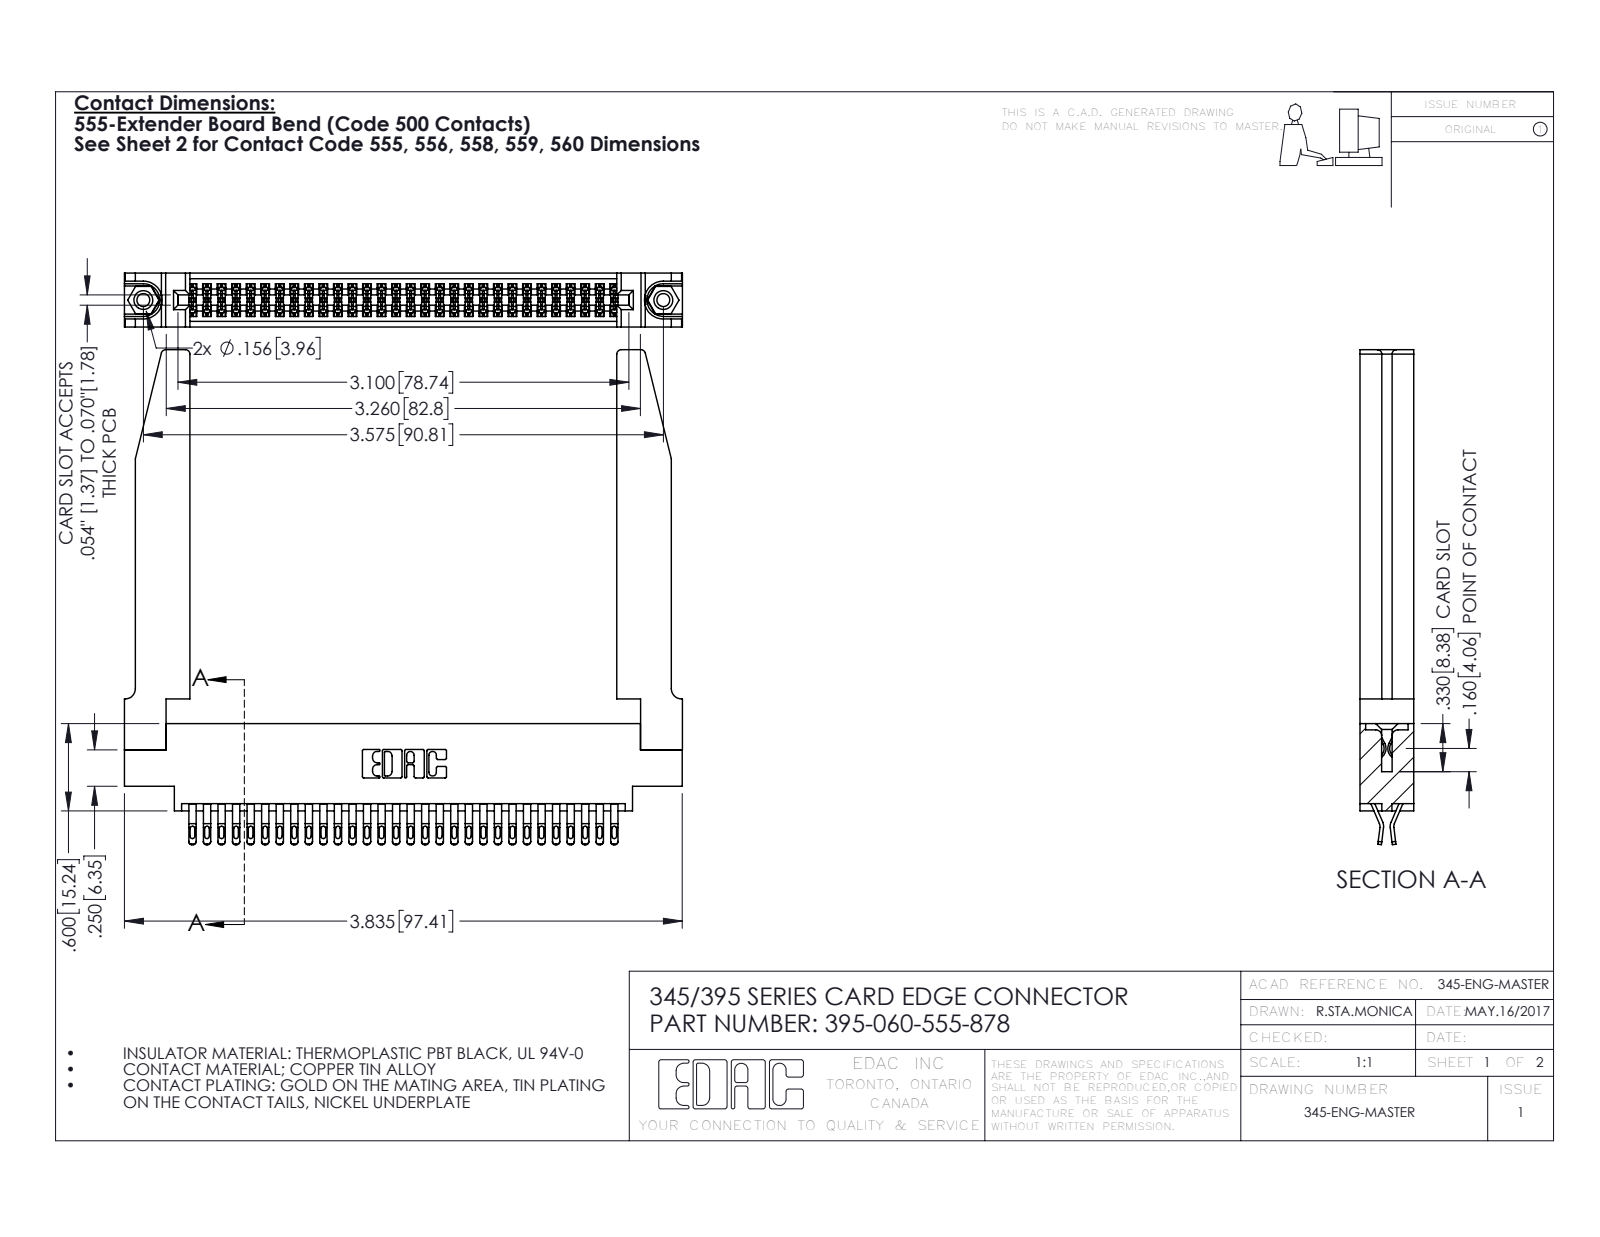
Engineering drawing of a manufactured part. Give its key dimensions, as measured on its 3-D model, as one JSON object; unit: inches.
{"part_name": "345-250-001_345-250-001-102; 345-292-001_555 Tail; 345 Part_0.170 Offset - 0.156 Dia-TH; 345-220-078_345-220-078 (+1 more)", "step_written_by": "SolidWorks 2016 (CONFIG_CONTROL_DESIGN)", "units": "inches", "bodies": {"solids": 65, "faces": 3724, "planar": 2086, "cylindrical": 1586, "other": 52}, "overall_size": [3.836, 3.402, 0.37], "volume_in3": 1.049, "surface_area_in2": 32.97, "round_holes": [[0.089, 2], [0.125, 2], [0.156, 2], [0.064, 1]], "round_bosses_or_shafts": [[0.155, 2]], "partial_cylinders_radius": [[0.016, 150], [0.02, 120], [0.006, 90], [0.01, 22], [0.03, 8], [0.007, 6], [0.031, 6], [0.026, 3]], "face_to_face_distances": [0.37, 0.072, 0.298, 0.025, 0.098, 0.272, 0.2, 0.225, 0.148, 0.15], "hole_center_spacings": [0.27, 3.34, 3.575]}
